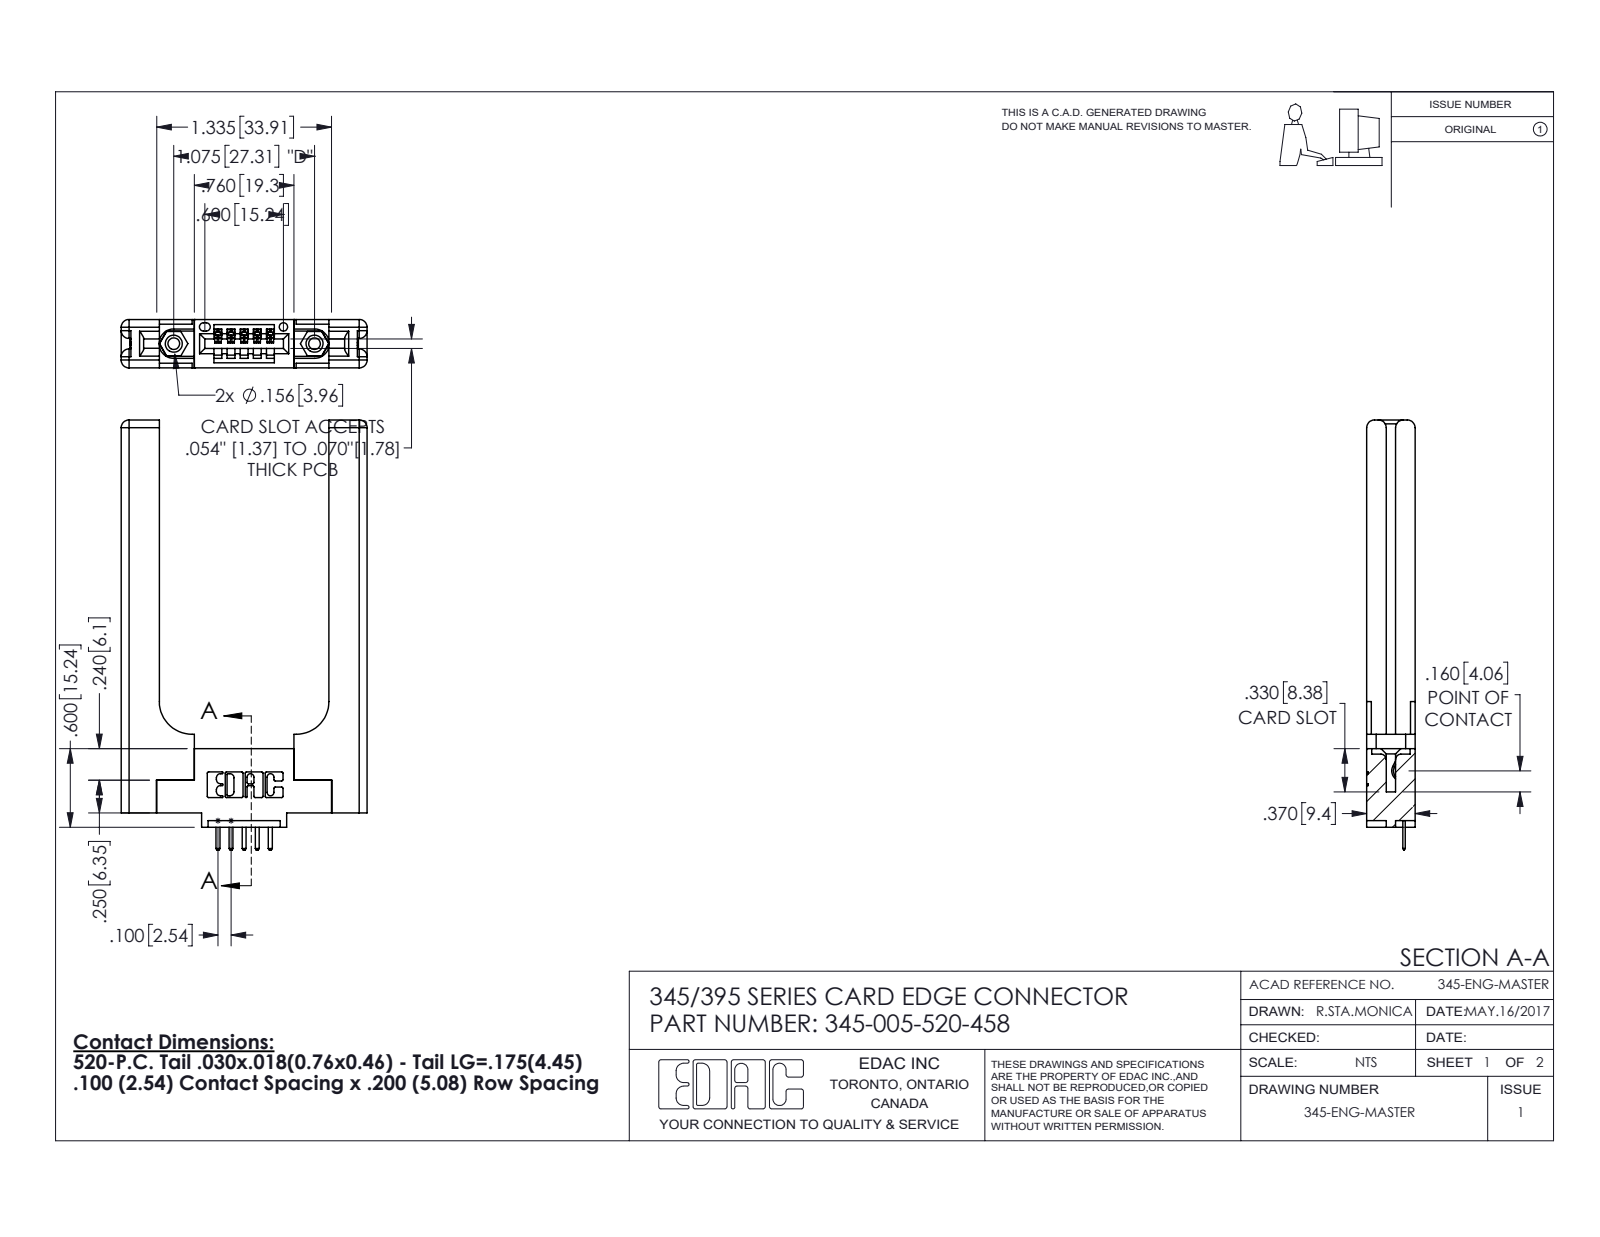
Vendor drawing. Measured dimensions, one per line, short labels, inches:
name: 345-005-520-458; 345 Part_0.110 Offset - 0.156 Dia-TH; 345-292-001_345-293-120; 345-250-001_345-250-001-102 (+1 more)
written by: SolidWorks 2016 (CONFIG_CONTROL_DESIGN)
unit: in
bodies: 10 solids, 696 faces (442 planar, 194 cylindrical, 60 other)
size: 3.285 × 1.879 × 0.37
volume: 0.772 in³; area: 16.03 in²
holes: 2× ⌀0.089, 2× ⌀0.125, 2× ⌀0.156, 1× ⌀0.064
bosses: 2× ⌀0.155
rounds: 22× R0.01, 16× R0.06, 12× R0.01, 10× R0.006, 6× R0.007, 6× R0.031, 3× R0.026, 2× R0.03
face distances: 0.37, 0.15, 0.22, 1.296, 0.072, 0.071, 0.292, 1.587, 0.298, 0.077
hole spacings: 0.27, 0.847, 1.075
